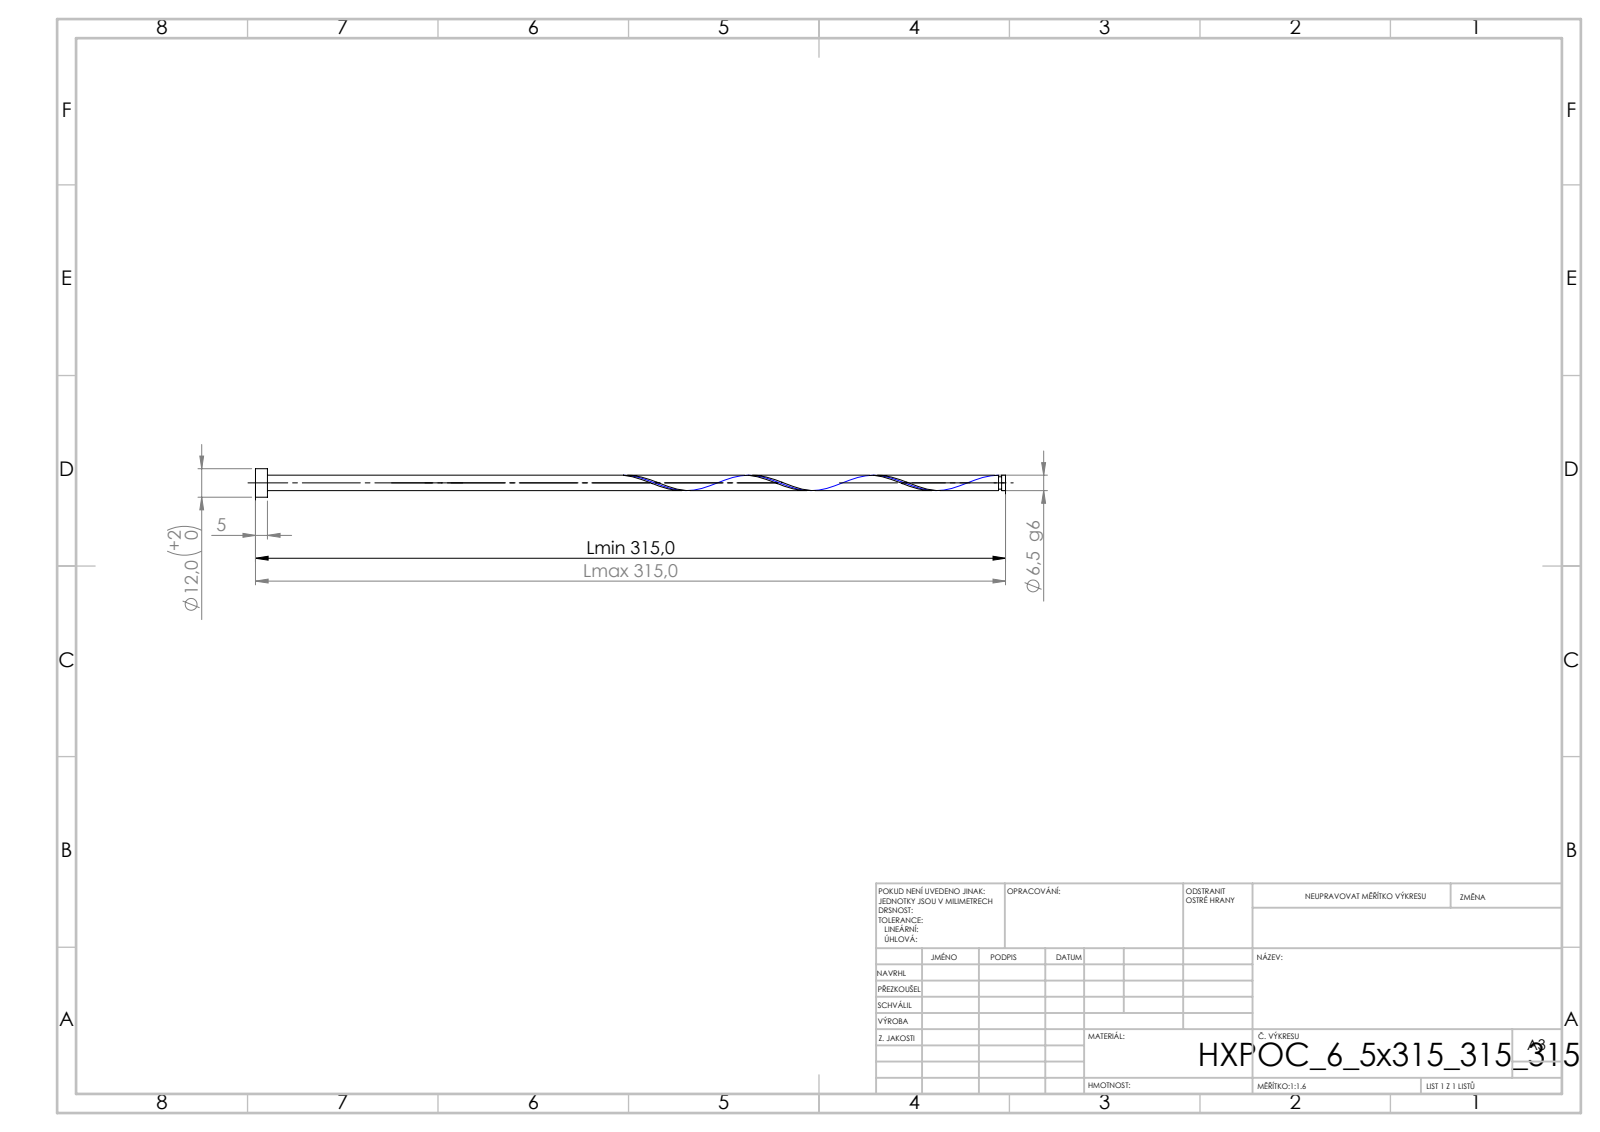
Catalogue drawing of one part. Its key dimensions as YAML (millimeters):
step_written_by: "SolidWorks 2019 (CONFIG_CONTROL_DESIGN)"
units: millimeters
bodies: {solids: 1, faces: 21, planar: 6, cylindrical: 14, other: 1}
overall_size: [315, 12, 12]
volume: 10737
surface_area: 6870
round_bosses_or_shafts:
  - {diameter: 12, count: 1}
  - {diameter: 6.5, count: 1}
  - {diameter: 5.2, count: 1}
face_to_face_distances: [5, 315, 310, 313.34, 308.34, 1.66, 312.04, 307.04, 1.3, 2.96]
